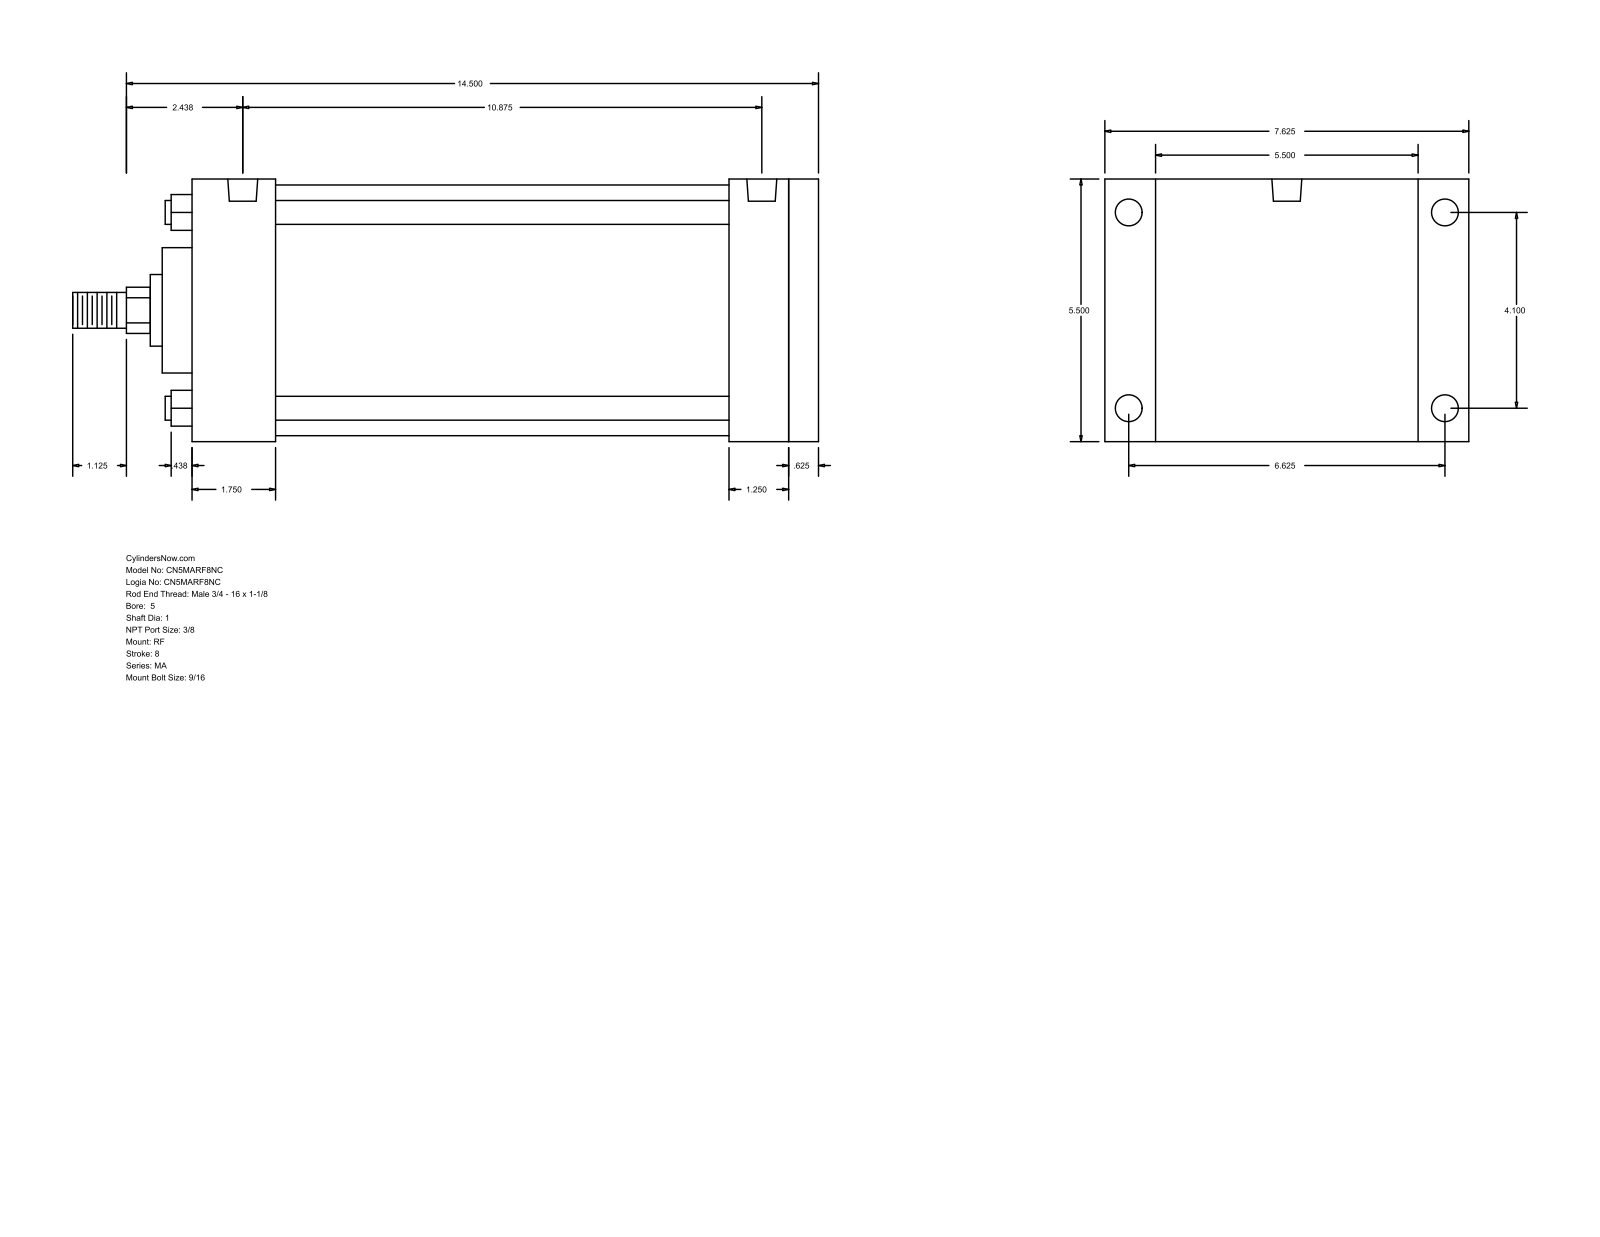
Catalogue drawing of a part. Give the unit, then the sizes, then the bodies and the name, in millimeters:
Units: millimetres
Overall size (bounding box): 396.88 × 193.68 × 139.7
Round holes (diameter × count): ⌀11.11 ×4, ⌀14.29 ×4, ⌀15.93 ×2
Round bosses / shafts (diameter × count): ⌀12.7 ×4, ⌀133.35 ×1, ⌀66.67 ×1, ⌀38.1 ×1, ⌀25.4 ×1, ⌀19.05 ×1
Partial cylindrical surfaces — rounded edges, fillets, slot ends (radius × count): R12.29 ×1
Main face-to-face distances: 139.7, 333.38, 15.87, 317.51, 47.62, 44.46, 273.05, 288.92, 285.76, 241.3
Hole centre spacings: 4.76, 104.14, 168.28, 197.9, 266.71, 271.47, 276.23
Bodies: 0 solids, 94 faces (65 planar, 29 cylindrical, 0 other)
Part name (STEP PRODUCT): MA_RF__0500_1
STEP written by: GSSL Pune (CONFIG_CONTROL_DESIGN)
